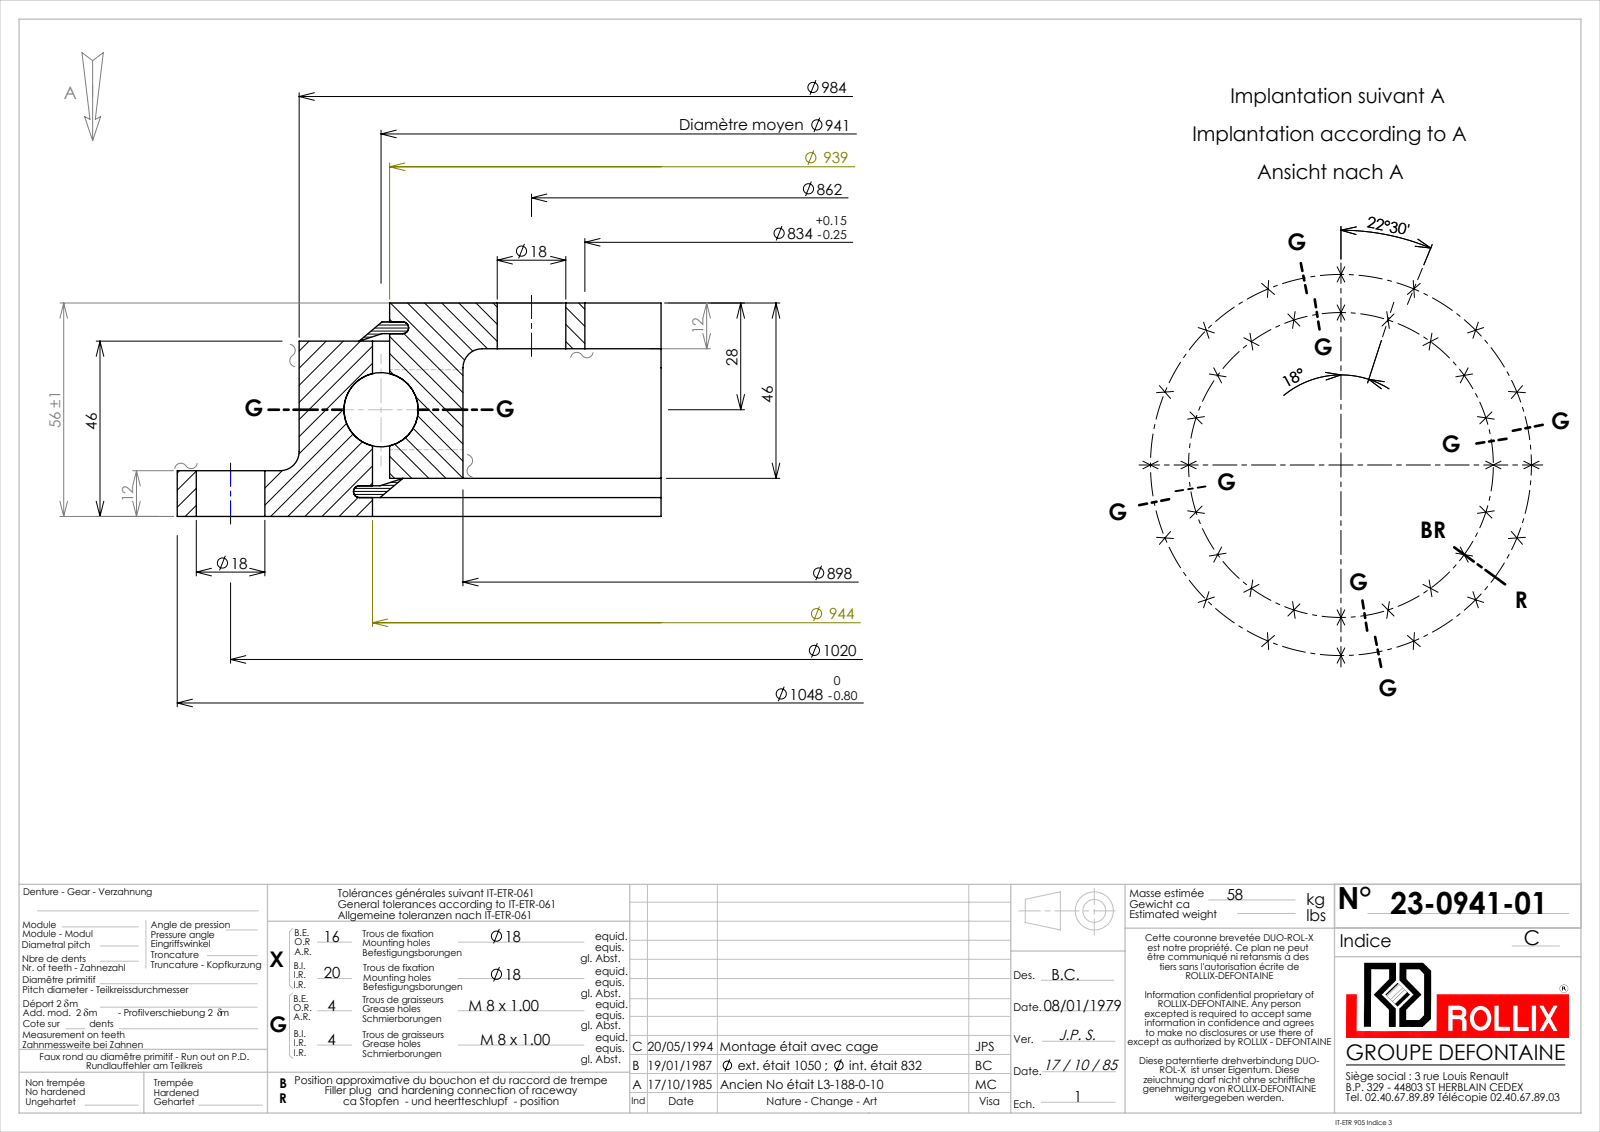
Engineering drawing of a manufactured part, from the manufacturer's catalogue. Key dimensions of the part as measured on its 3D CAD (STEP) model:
Part name (STEP PRODUCT): 23-0941-01
STEP written by: SolidWorks 2016 (CONFIG_CONTROL_DESIGN)
Units: millimetres
Bodies: 13 solids, 330 faces (94 planar, 124 cylindrical, 112 other)
Overall size (bounding box): 1048 × 1048 × 56
Volume: 6 899 000 mm³ · Surface area: 1 420 000 mm²
Round holes (diameter × count): ⌀18 ×36, ⌀7 ×8, ⌀834 ×1, ⌀898 ×1, ⌀945.5 ×1
Round bosses / shafts (diameter × count): ⌀8 ×8, ⌀1048 ×1, ⌀984 ×1, ⌀936.5 ×1
Main face-to-face distances: 12, 44, 56, 10, 46, 2, 34, 32, 36, 8.05
Hole centre spacings: 134.85, 609.53, 697.38, 819.82, 431.01, 266.38, 391.34, 506.68
